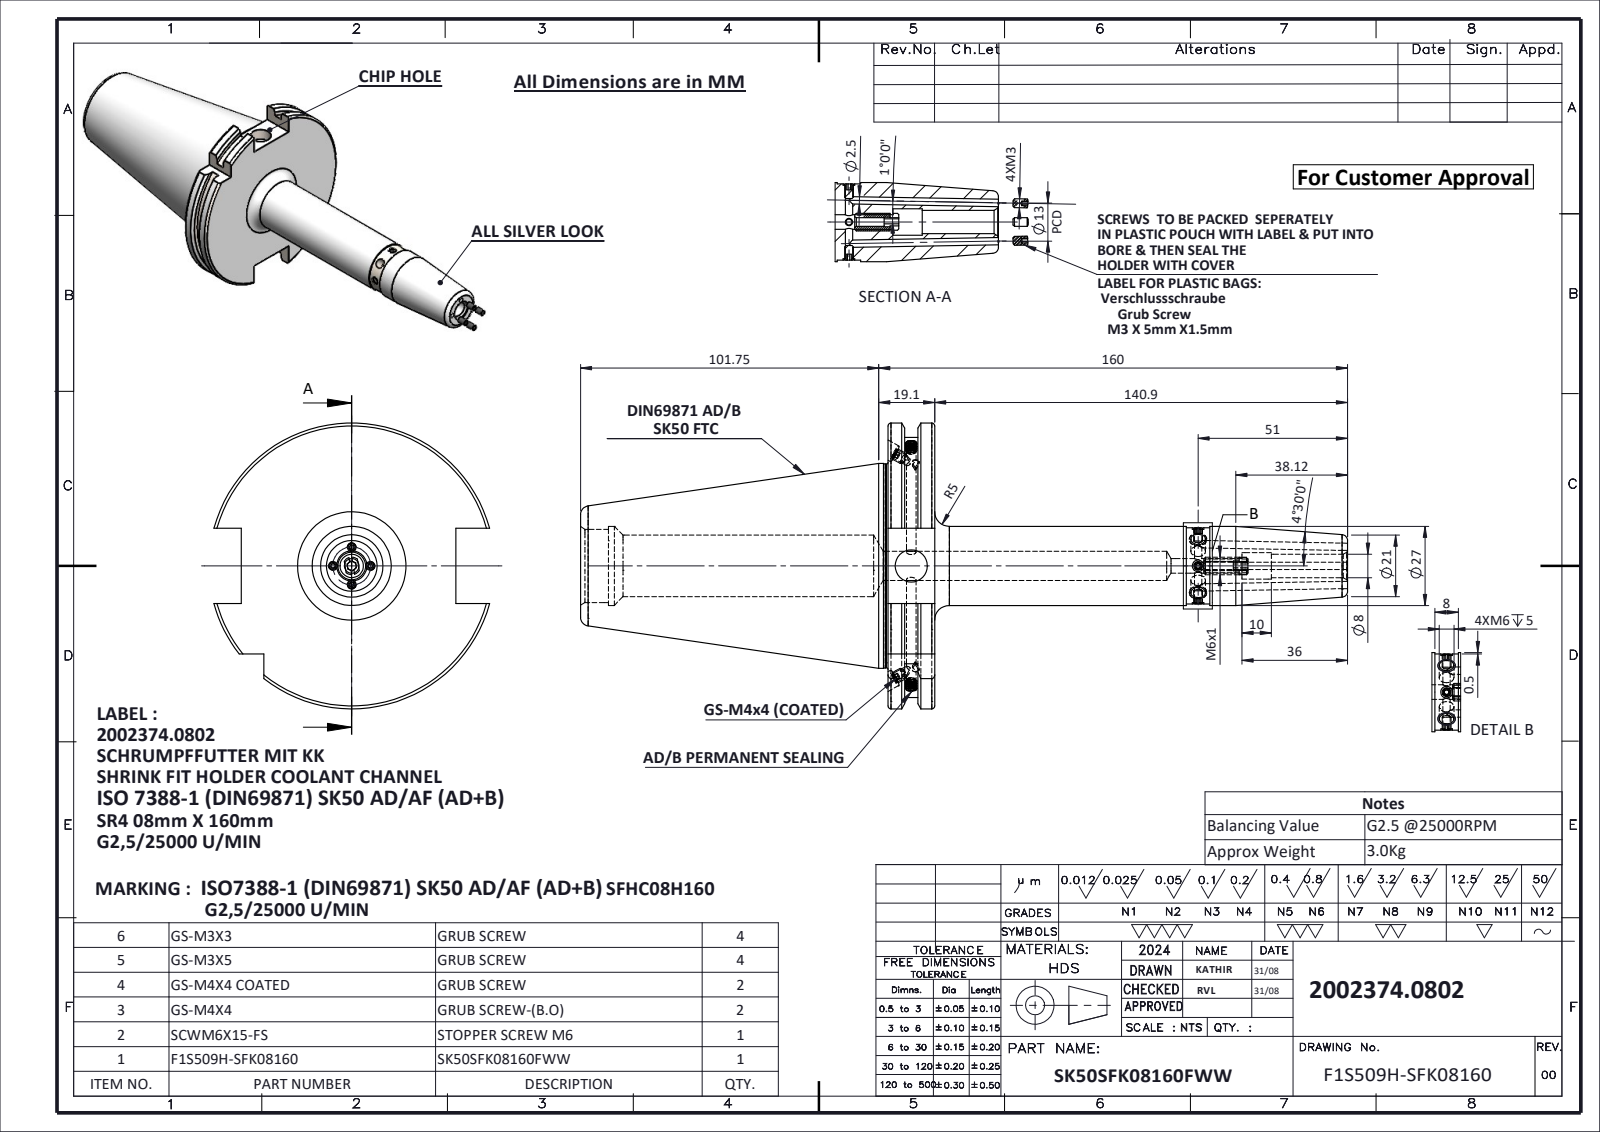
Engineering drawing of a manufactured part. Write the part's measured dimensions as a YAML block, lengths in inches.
part_name: "GS-M4X4_DIN 913 - M4 x 4-N; GS-M4X4-COATING_DIN 913 - M4 x 4-N; F1S509H-SFK08160; SK50SFK08160FWW (+3 more)"
step_written_by: "SolidWorks 2024 (CONFIG_CONTROL_DESIGN)"
units: inches
bodies: {solids: 14, faces: 493, planar: 188, cylindrical: 141, other: 164}
overall_size: [10.7, 3.839, 3.703]
volume: 23.77
surface_area: 98.17
round_holes:
  - {diameter: 0.098, count: 6}
  - {diameter: 0.197, count: 5}
  - {diameter: 0.126, count: 2}
  - {diameter: 0.157, count: 2}
  - {diameter: 0.236, count: 2}
  - {diameter: 0.118, count: 1}
  - {diameter: 0.13, count: 1}
  - {diameter: 0.315, count: 1}
  - {diameter: 0.354, count: 1}
  - {diameter: 0.394, count: 1}
  - {diameter: 0.433, count: 1}
  - {diameter: 0.827, count: 1}
round_bosses_or_shafts:
  - {diameter: 0.118, count: 6}
  - {diameter: 0.157, count: 4}
  - {diameter: 0.114, count: 2}
  - {diameter: 2.75, count: 1}
  - {diameter: 2.734, count: 1}
  - {diameter: 1.063, count: 1}
  - {diameter: 1.024, count: 1}
partial_cylinders:
  - {radius: 0.118, count: 1}
  - {radius: 1.768, count: 1}
  - {radius: 1.919, count: 1}
face_to_face_distances: [0.626, 0.223, 0.403, 0.399, 0.176, 0.227, 4.132, 4.355, 4.531, 4.758]
hole_center_spacings: [3.854]
